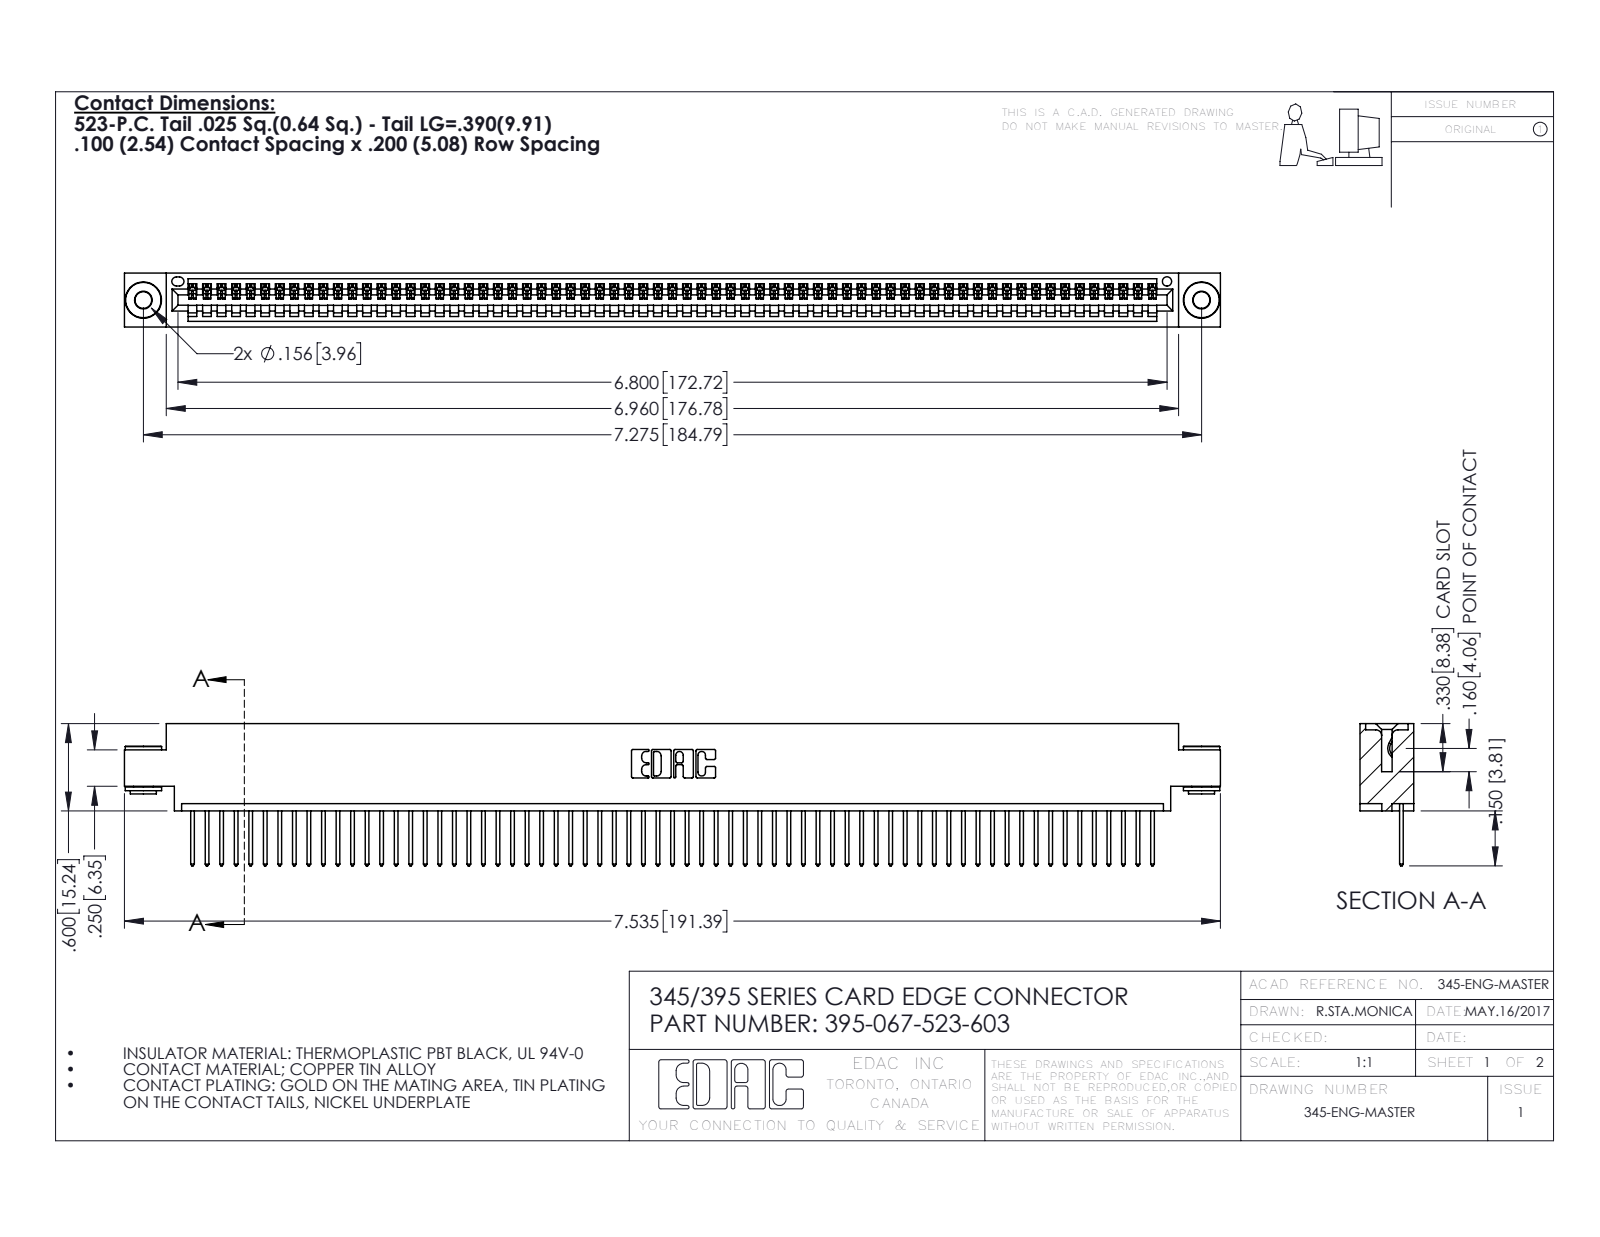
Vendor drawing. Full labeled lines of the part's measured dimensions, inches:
Part name (STEP PRODUCT): 345-250-002_345-250-002-102; 345 Part_0.170 Offset - 0.156 Dia-TH; 395-067-523-603; 345-292-001_345-293-123
STEP written by: SolidWorks 2016 (CONFIG_CONTROL_DESIGN)
Units: inches
Bodies: 70 solids, 4054 faces (2774 planar, 1272 cylindrical, 8 other)
Overall size (bounding box): 7.535 × 0.977 × 0.37
Volume: 1.114 in³ · Surface area: 38.79 in²
Round holes (diameter × count): ⌀0.116 ×2, ⌀0.156 ×2, ⌀0.064 ×1
Round bosses / shafts (diameter × count): ⌀0.25 ×2, ⌀0.18 ×2, ⌀0.136 ×2
Partial cylindrical surfaces — rounded edges, fillets, slot ends (radius × count): R0.006 ×134, R0.01 ×134, R0.01 ×22, R0.007 ×6, R0.031 ×6, R0.026 ×3, R0.031 ×2, R0.04 ×2
Main face-to-face distances: 0.072, 0.298, 0.37, 0.098, 0.272, 0.025, 0.2, 0.225, 0.175, 0.149
Hole centre spacings: 0.27, 7.039, 7.275
